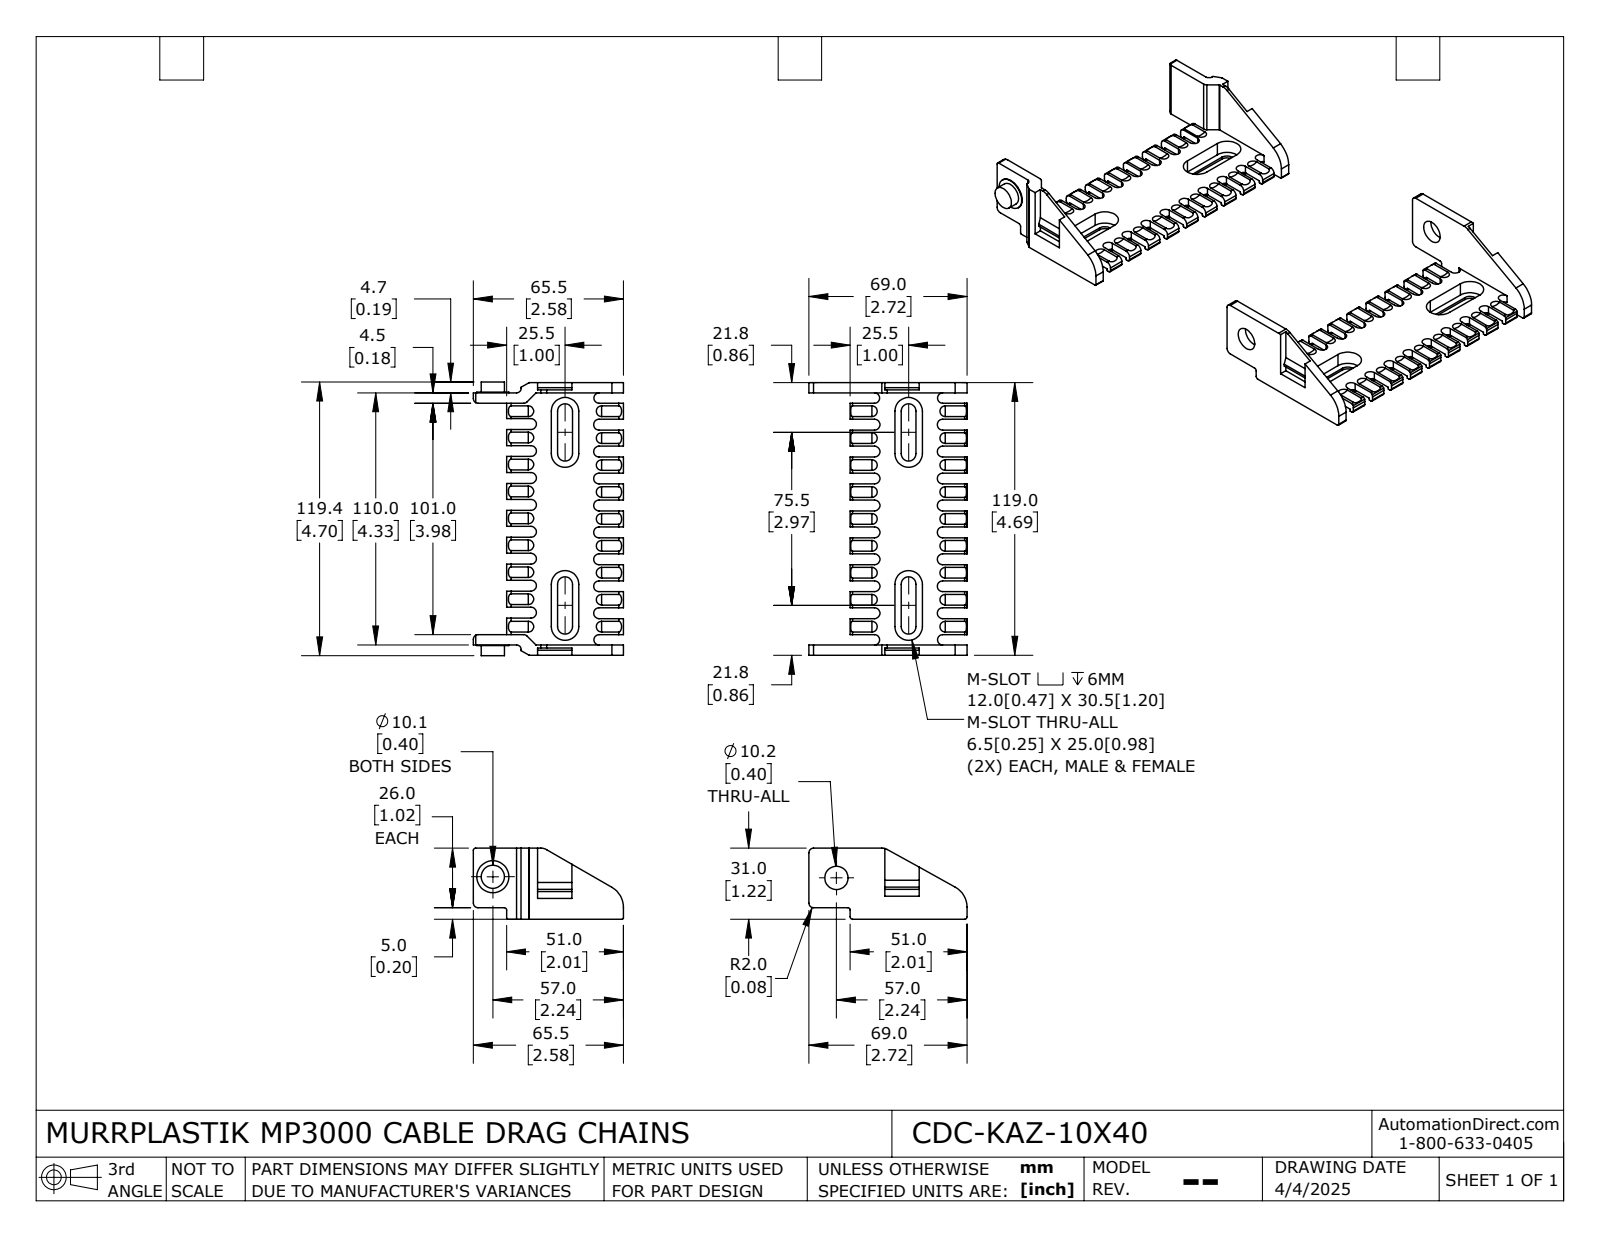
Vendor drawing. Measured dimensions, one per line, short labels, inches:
name: CDC-KAZ-10X40
written by: SolidWorks 2024 (AUTOMOTIVE_DESIGN)
unit: in
bodies: 2 solids, 643 faces (330 planar, 277 cylindrical, 36 other)
size: 8.484 × 4.701 × 1.22
volume: 4.217 in³; area: 63.52 in²
holes: 1× ⌀0.402
bosses: 1× ⌀0.551, 1× ⌀0.398
rounds: 32× R0.094, 16× R0.276, 15× R0.039, 13× R0.079, 8× R0.128, 8× R0.236, 6× R0.089, 4× R0.02
face distances: 0.276, 0.177, 0.138, 4.508, 4.331, 4.685, 0.354, 4.154, 0.463, 0.098
